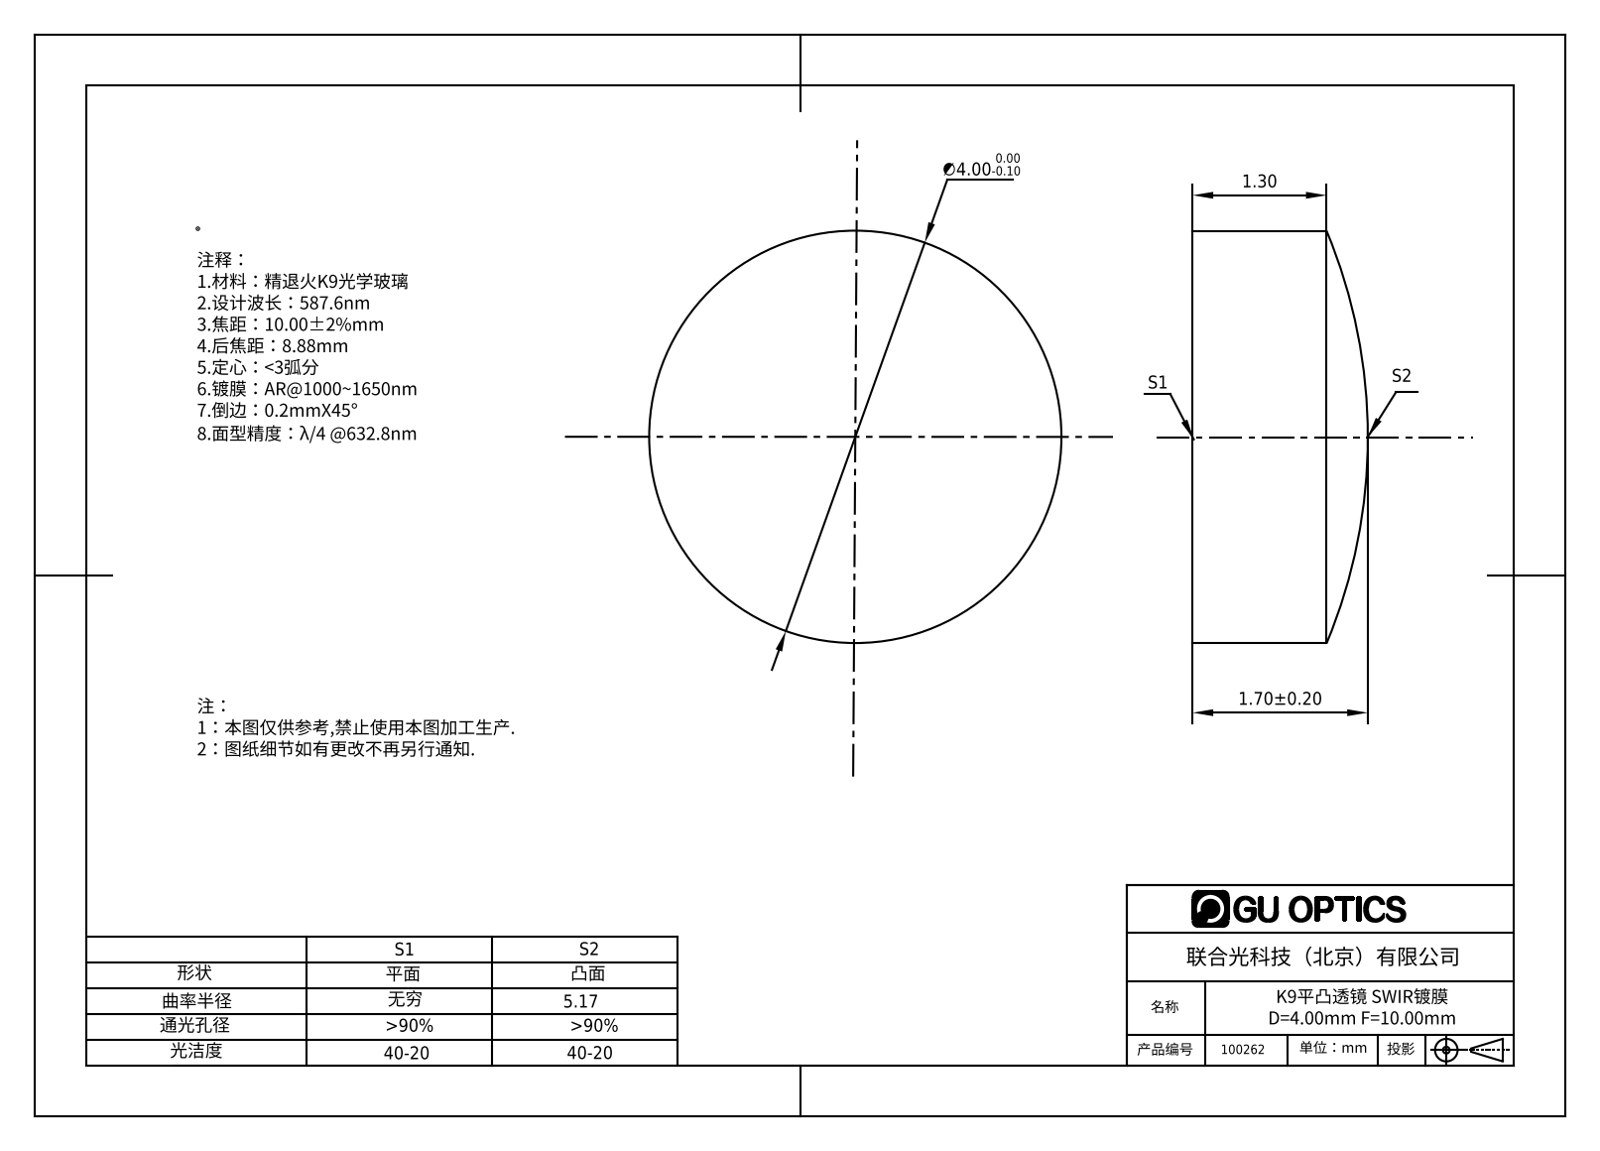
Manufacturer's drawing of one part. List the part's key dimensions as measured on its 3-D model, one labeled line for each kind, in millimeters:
Part name (STEP PRODUCT): 100090
STEP written by: SolidWorks 2016 (AUTOMOTIVE_DESIGN)
Units: millimetres
Bodies: 1 solid, 5 faces (1 planar, 2 cylindrical, 2 other)
Overall size (bounding box): 4 × 4 × 1.7
Volume: 19 mm³ · Surface area: 42 mm²
Round bosses / shafts (diameter × count): ⌀4 ×1
